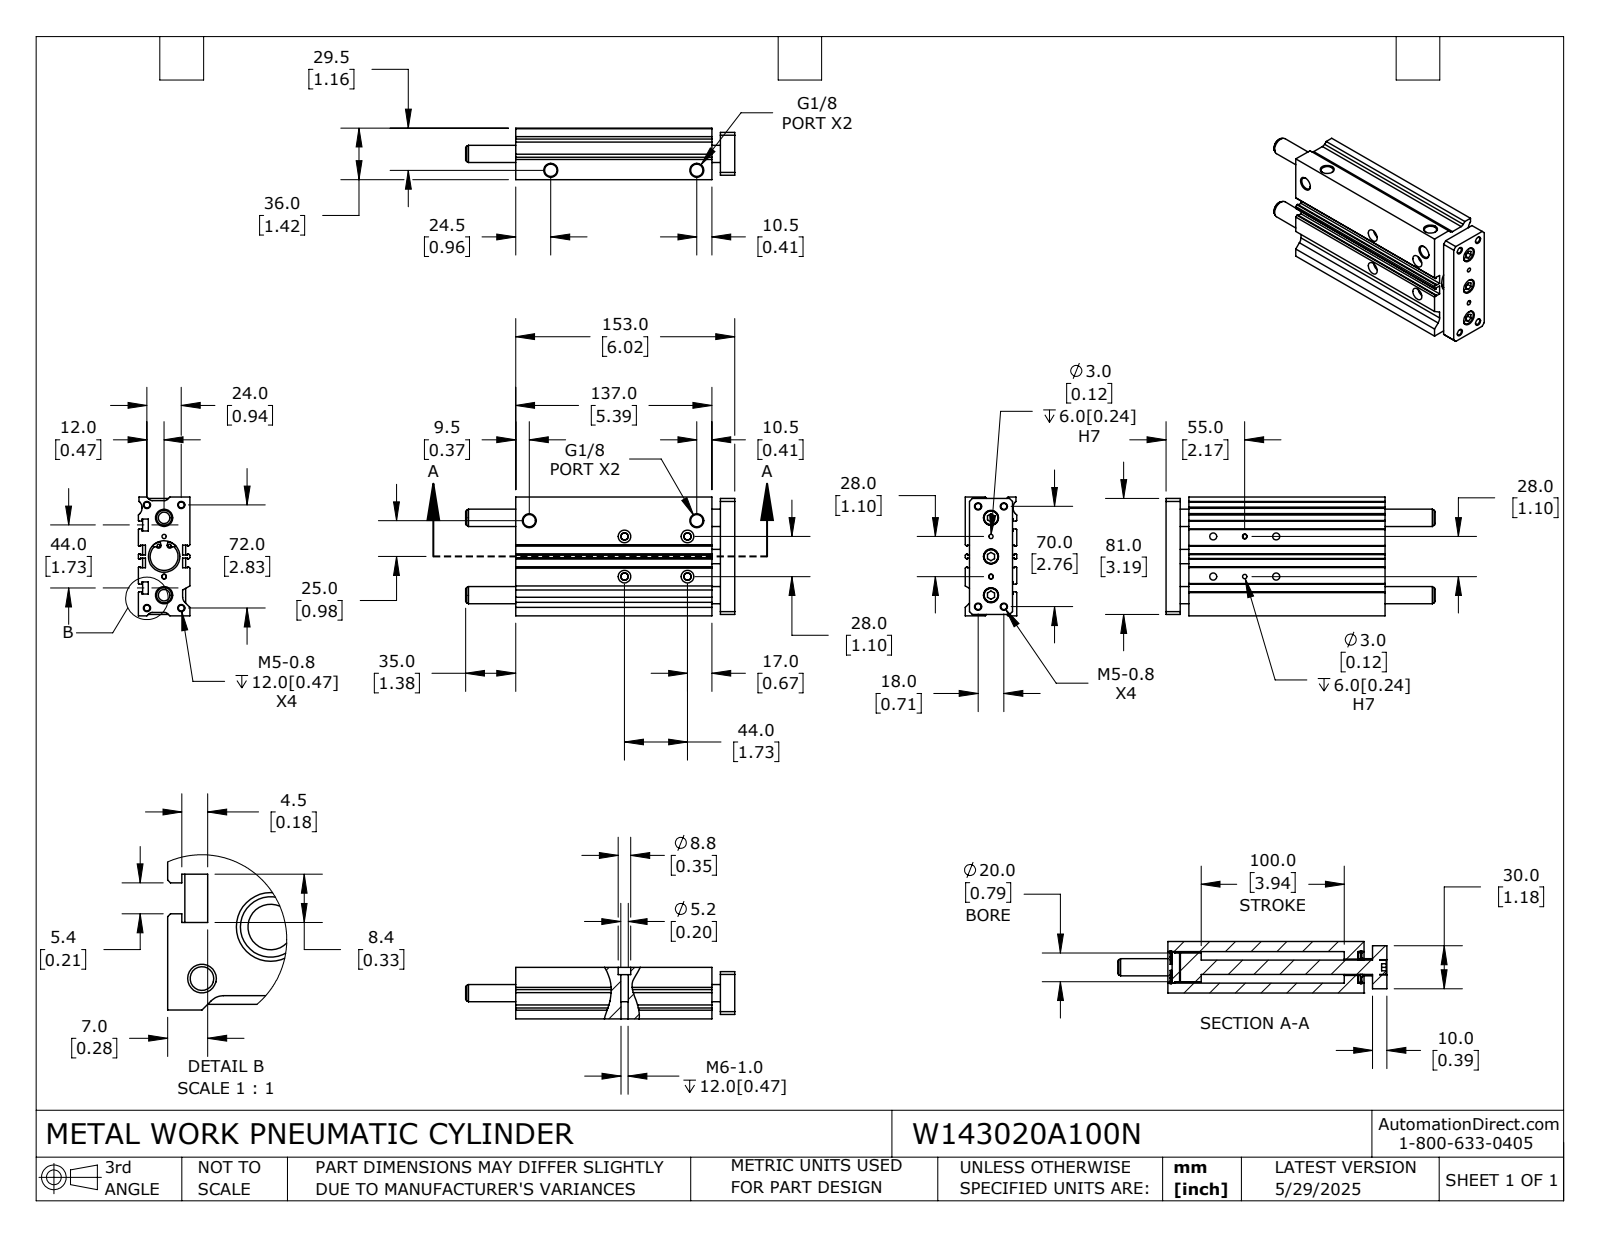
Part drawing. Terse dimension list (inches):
name: W143020A100N_ROD; W143020A100N_BODY; W143020A100N
written by: SolidWorks 2024 (CONFIG_CONTROL_DESIGN)
unit: in
bodies: 6 solids, 357 faces (174 planar, 145 cylindrical, 38 other)
size: 7.402 × 3.268 × 1.417
volume: 21.47 in³; area: 160.8 in²
holes: 8× ⌀0.163, 4× ⌀0.079, 4× ⌀0.118, 4× ⌀0.205, 4× ⌀0.337, 4× ⌀0.346, 3× ⌀0.413, 2× ⌀0.194, 2× ⌀0.194, 2× ⌀0.472, 1× ⌀0.449, 1× ⌀0.767
bosses: 3× ⌀0.394, 2× ⌀0.906, 1× ⌀0.787, 1× ⌀0.512
rounds: 4× R0.053, 4× R0.059, 4× R0.071, 4× R0.118, 3× R0.197
face distances: 1.417, 0.098, 0.197, 1.22, 0.079, 1.024, 3.268, 0.276, 3.169, 0.945
hole spacings: 0.124, 0.296, 0.336, 0.474, 0.591, 0.78, 0.828, 0.864
